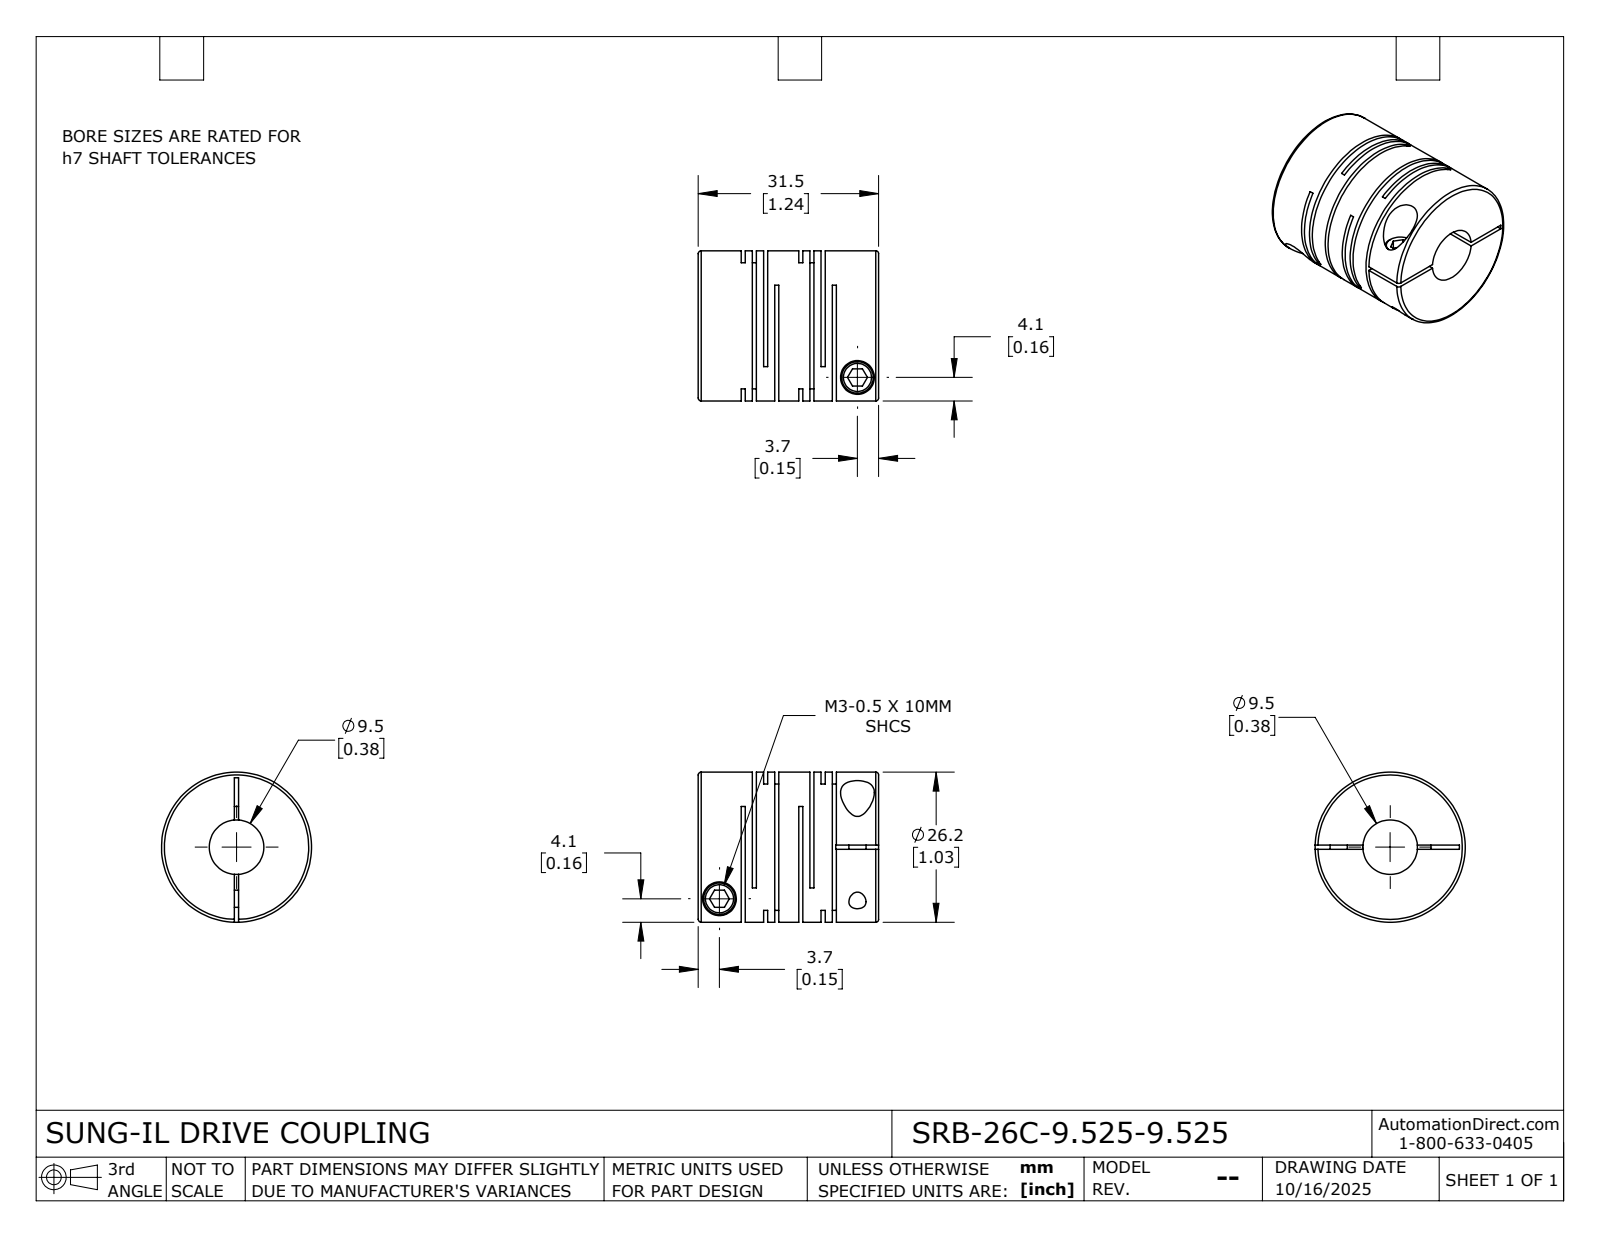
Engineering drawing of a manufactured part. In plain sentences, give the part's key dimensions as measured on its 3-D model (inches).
The part is named "SRB-26C-9.525-9.525". Its 3-D file was written by "SolidWorks 2024 (CONFIG_CONTROL_DESIGN)". It is 1 solid with 115 faces: 60 planar, 42 cylindrical and 13 other. Overall it measures 1.24 by 1.031 by 1.031 inches. Its volume is 0.74 cubic inches and its surface area 16.78 square inches. Round holes: 2 of diameter 0.118, 2 of diameter 0.232, 1 of diameter 0.375. Round bosses or shafts: 2 of diameter 0.217, 1 of diameter 1.031. The main face-to-face distances are 0.077, 0.396, 0.028, 0.154, 0.319, 0.472, 0.049, 0.105, 0.368, 0.549.
